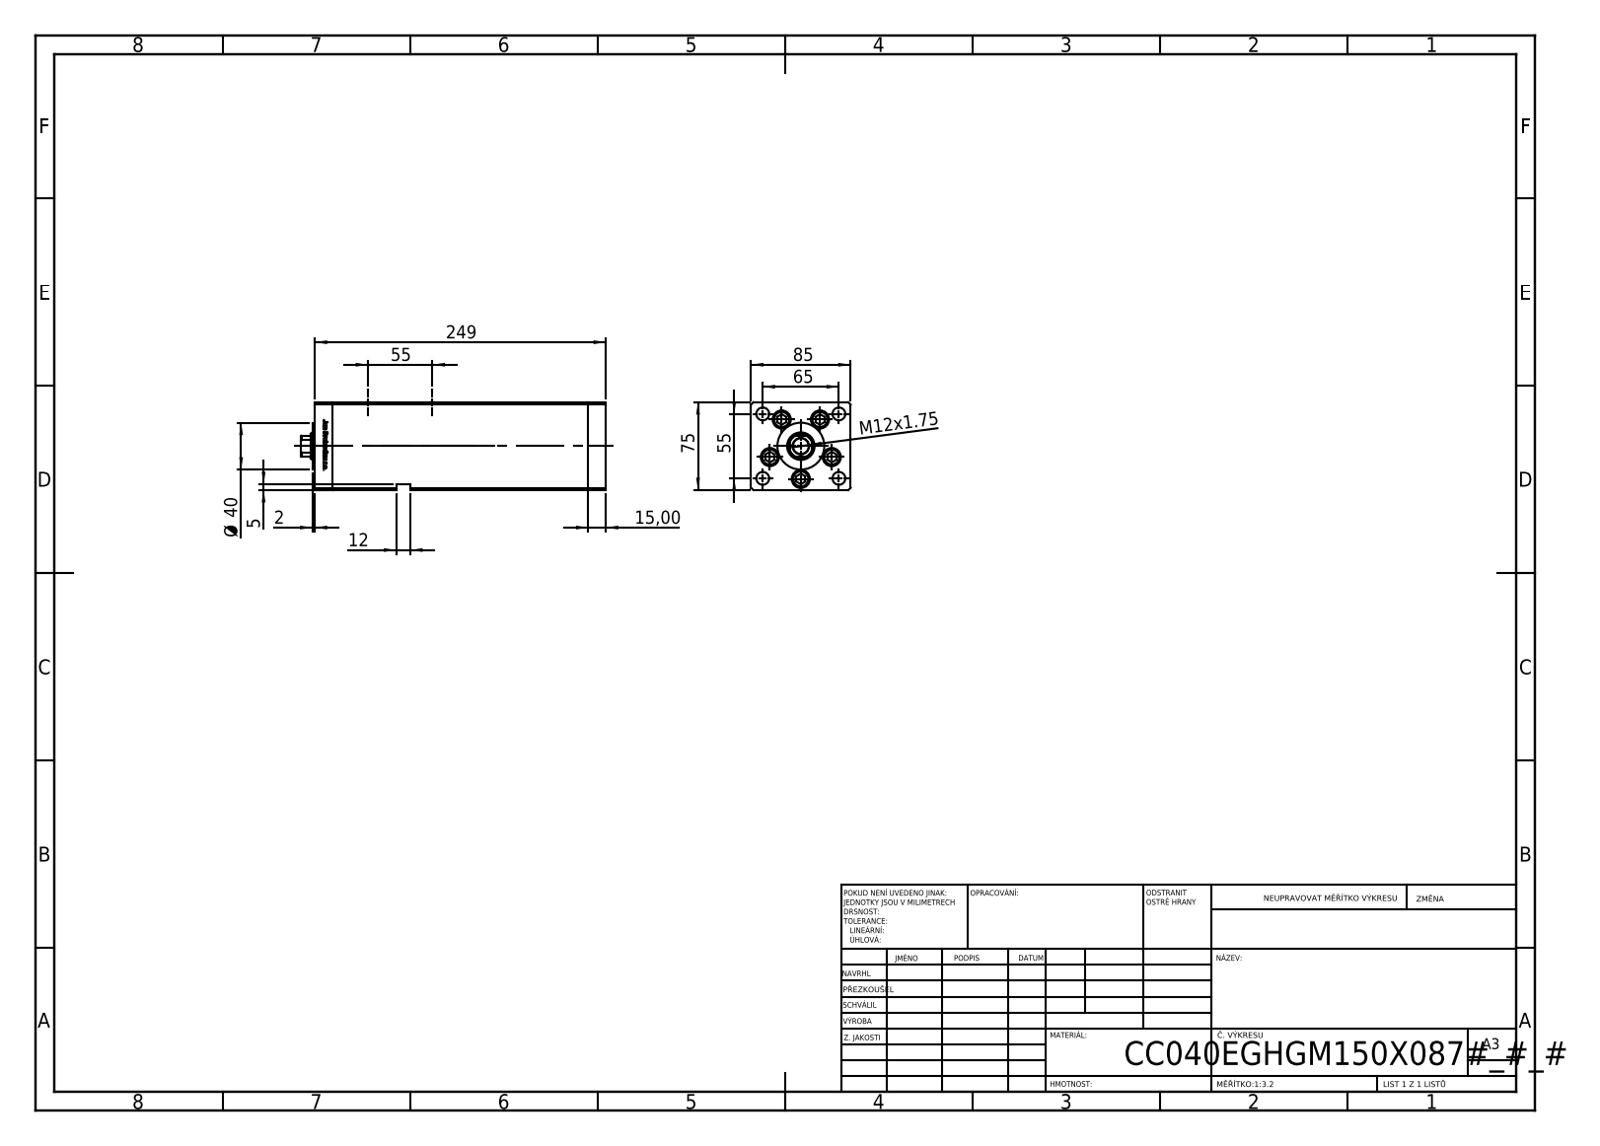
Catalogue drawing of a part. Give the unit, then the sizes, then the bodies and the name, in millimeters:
Units: millimetres
Overall size (bounding box): 260 × 85 × 75
Round holes (diameter × count): ⌀11 ×9, ⌀15.5 ×5, ⌀10.5 ×4, ⌀16.5 ×4, ⌀2 ×2, ⌀13.16 ×2, ⌀13.5 ×1, ⌀22 ×1, ⌀23.5 ×1
Round bosses / shafts (diameter × count): ⌀14.5 ×5, ⌀8 ×5, ⌀40 ×1
Partial cylindrical surfaces — rounded edges, fillets, slot ends (radius × count): R0.93 ×2, R10.5 ×1
Main face-to-face distances: 85, 75, 15, 218.5, 233.5, 248.5, 68.5, 10.5, 34.25, 64.5
Hole centre spacings: 28, 42.57, 55, 65, 85.15, 16.86, 19.17, 32.33
Volume: 1 341 000 mm³ · Surface area: 209 531 mm²
Bodies: 14 solids, 1212 faces (473 planar, 165 cylindrical, 574 other)
Part name (STEP PRODUCT): ALLEN BOLT; V220C BACK_E; V220C_E MIDDLE; V220C_FRONT_E (+1 more)
STEP written by: SolidWorks 2019 (CONFIG_CONTROL_DESIGN)
